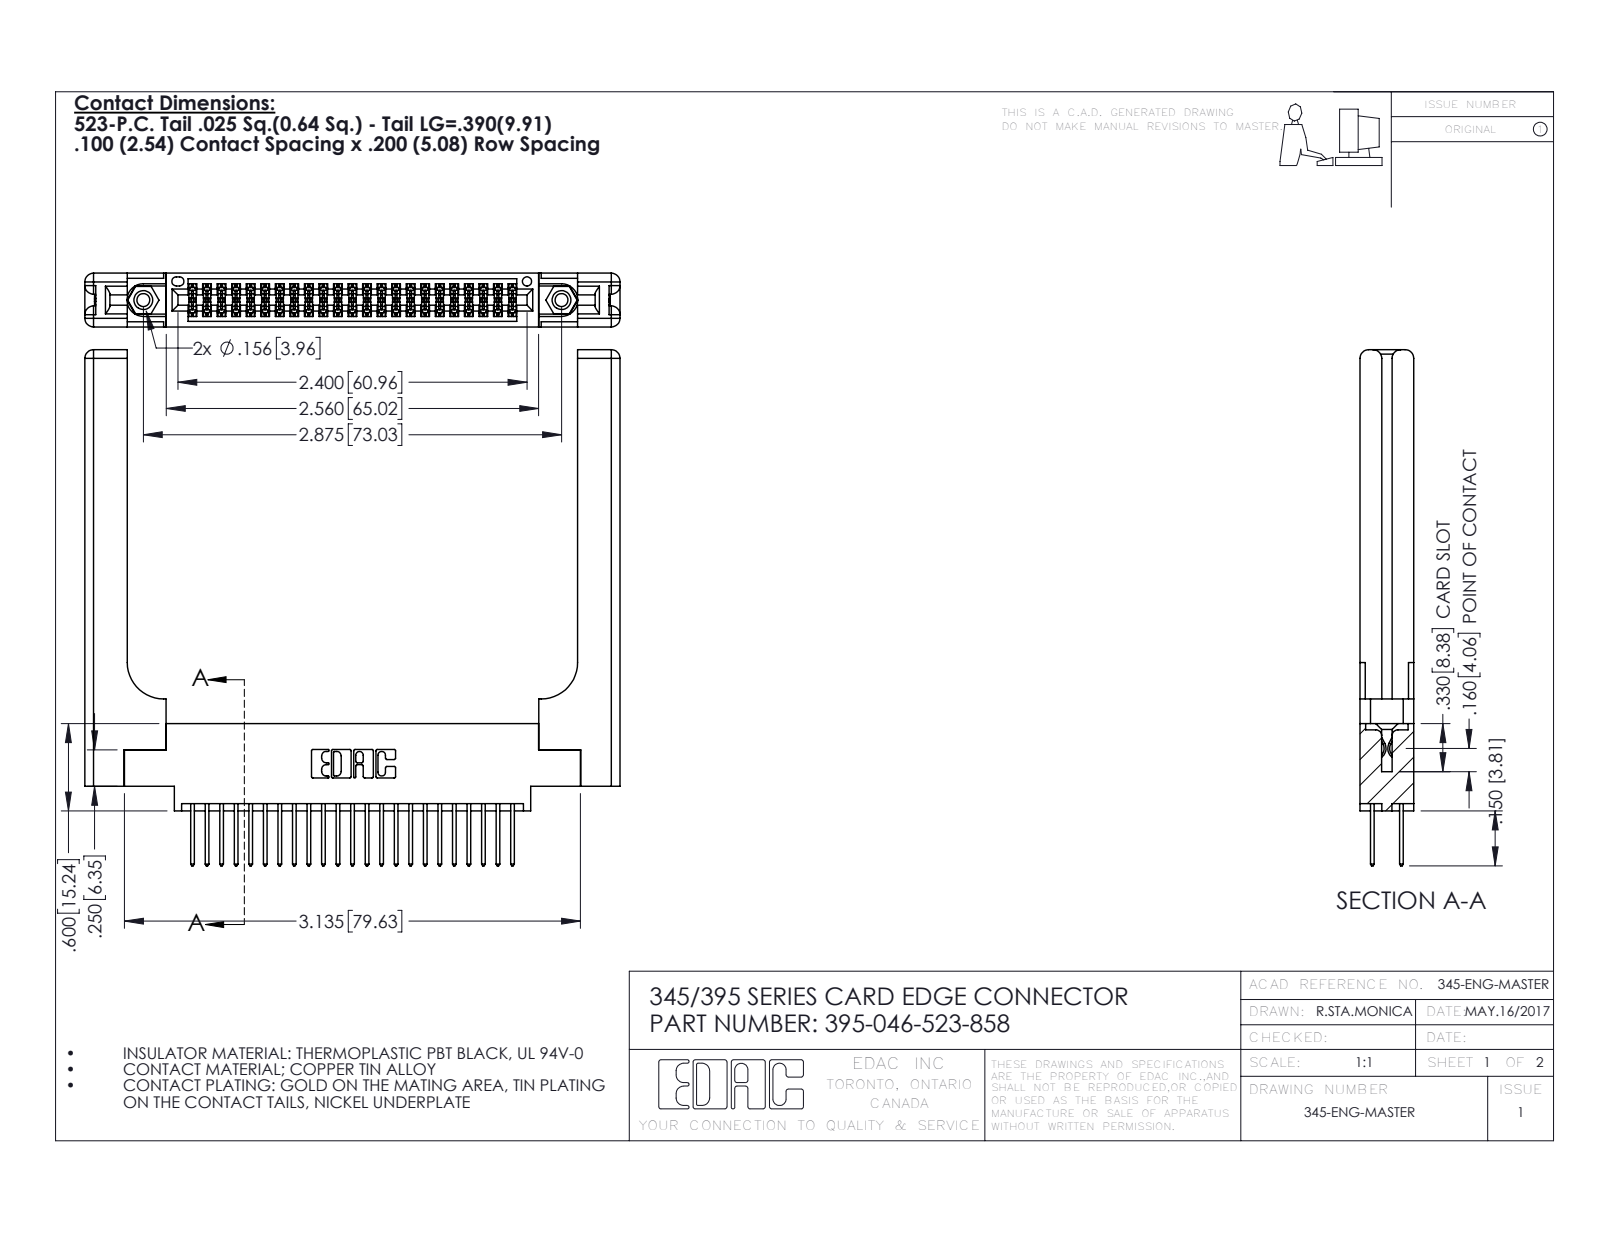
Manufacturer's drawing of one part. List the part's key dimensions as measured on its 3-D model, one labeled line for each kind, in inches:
Part name (STEP PRODUCT): 345-250-001_345-250-001-102; 345 Part_0.170 Offset - 0.156 Dia-TH; 395-046-523-858; 345-292-001_345-293-123 (+1 more)
STEP written by: SolidWorks 2016 (CONFIG_CONTROL_DESIGN)
Units: inches
Bodies: 51 solids, 2686 faces (1750 planar, 876 cylindrical, 60 other)
Overall size (bounding box): 3.679 × 3.547 × 0.37
Volume: 1.059 in³ · Surface area: 28.5 in²
Round holes (diameter × count): ⌀0.089 ×2, ⌀0.125 ×2, ⌀0.156 ×2, ⌀0.064 ×1
Round bosses / shafts (diameter × count): ⌀0.155 ×2
Partial cylindrical surfaces — rounded edges, fillets, slot ends (radius × count): R0.006 ×69, R0.01 ×46, R0.01 ×22, R0.06 ×16, R0.007 ×6, R0.031 ×6, R0.026 ×3, R0.014 ×2
Main face-to-face distances: 0.37, 0.072, 0.298, 0.098, 0.272, 0.025, 0.2, 0.225, 0.15, 0.148
Hole centre spacings: 0.27, 2.641, 2.875
